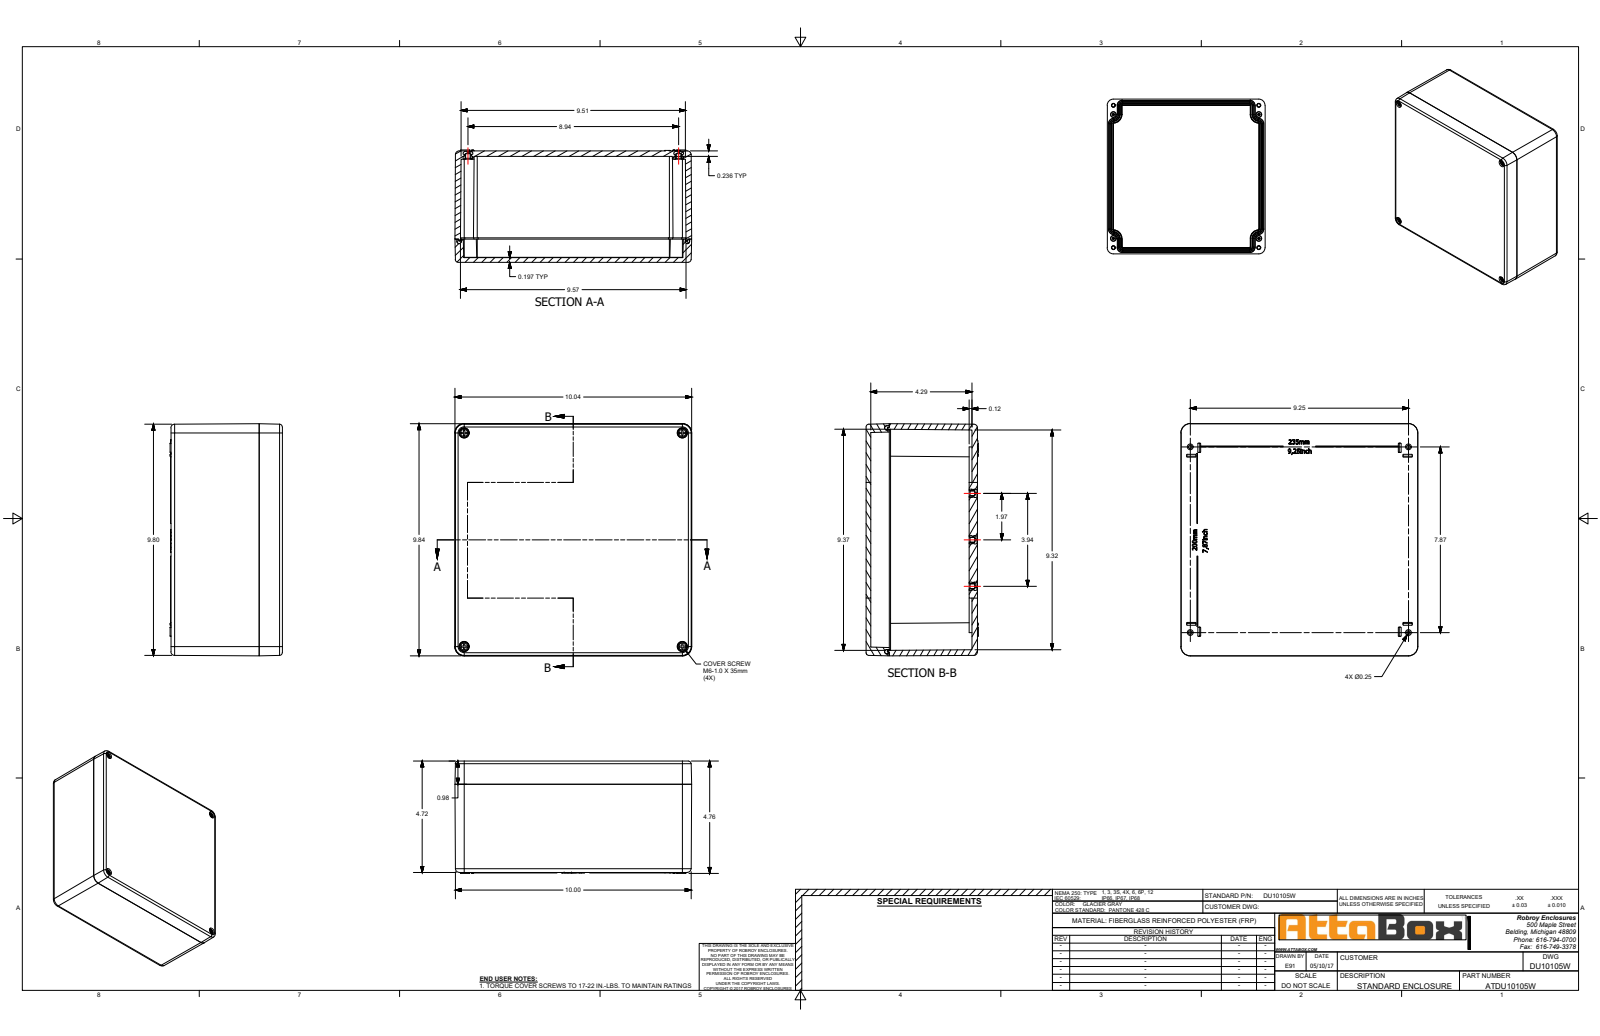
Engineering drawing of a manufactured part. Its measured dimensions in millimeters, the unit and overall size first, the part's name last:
Units: millimetres
Overall size (bounding box): 255 × 250 × 121
Round holes (diameter × count): ⌀4.9 ×6, ⌀6 ×6, ⌀4.9 ×4, ⌀5.4 ×4, ⌀7 ×4
Round bosses / shafts (diameter × count): ⌀7.4 ×10, ⌀9.5 ×4, ⌀8 ×4, ⌀6 ×4, ⌀5.2 ×4
Partial cylindrical surfaces — rounded edges, fillets, slot ends (radius × count): R0.5 ×32, R2.3 ×12, R4.2 ×8, R8.7 ×8, R0.4 ×6, R3 ×4, R3.3 ×4, R3.3 ×4
Main face-to-face distances: 120, 115, 5, 114, 6, 109, 25, 20, 89, 95
Hole centre spacings: 50, 65.1, 115.1, 165, 232.4, 240, 258, 283.9
Volume: 1 532 000 mm³ · Surface area: 535 900 mm²
Bodies: 17 solids, 1263 faces (615 planar, 170 cylindrical, 478 other)
Part name (STEP PRODUCT): DU10105W
STEP written by: SolidWorks 2018 (AUTOMOTIVE_DESIGN)
